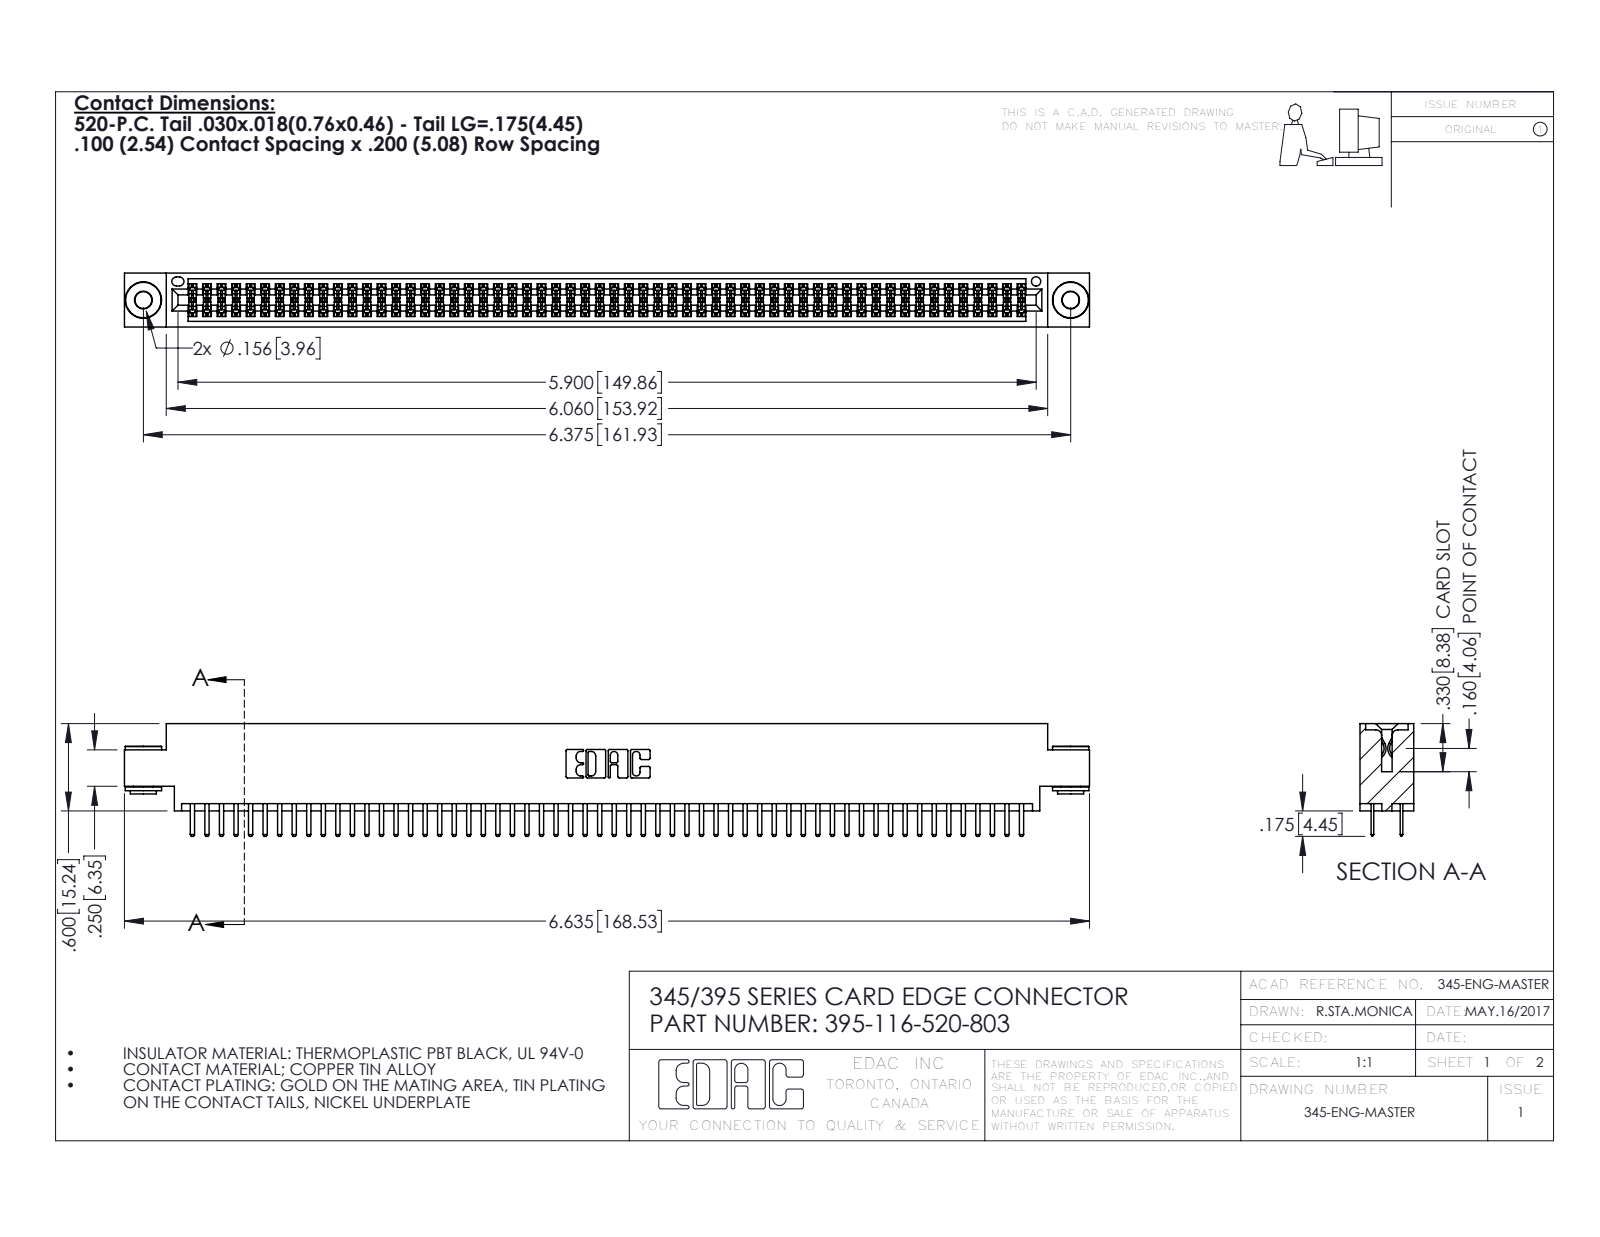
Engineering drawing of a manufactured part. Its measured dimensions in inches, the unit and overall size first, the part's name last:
Units: inches
Overall size (bounding box): 6.635 × 0.775 × 0.37
Round holes (diameter × count): ⌀0.116 ×2, ⌀0.156 ×2, ⌀0.064 ×1
Round bosses / shafts (diameter × count): ⌀0.25 ×2, ⌀0.18 ×2, ⌀0.136 ×2
Partial cylindrical surfaces — rounded edges, fillets, slot ends (radius × count): R0.006 ×174, R0.01 ×120, R0.01 ×22, R0.007 ×6, R0.031 ×6, R0.026 ×3, R0.014 ×2, R0.019 ×2
Main face-to-face distances: 0.072, 0.298, 0.2, 0.37, 0.098, 0.272, 0.025, 0.225, 0.022, 0.175
Hole centre spacings: 0.27, 6.139, 6.375
Volume: 0.999 in³ · Surface area: 38.37 in²
Bodies: 119 solids, 6432 faces (4154 planar, 2270 cylindrical, 8 other)
Part name (STEP PRODUCT): 345-292-001_345-293-120; 395-116-520-803; 345 Part_0.170 Offset - 0.156 Dia-TH; 345-250-002_345-250-002-102
STEP written by: SolidWorks 2016 (CONFIG_CONTROL_DESIGN)
